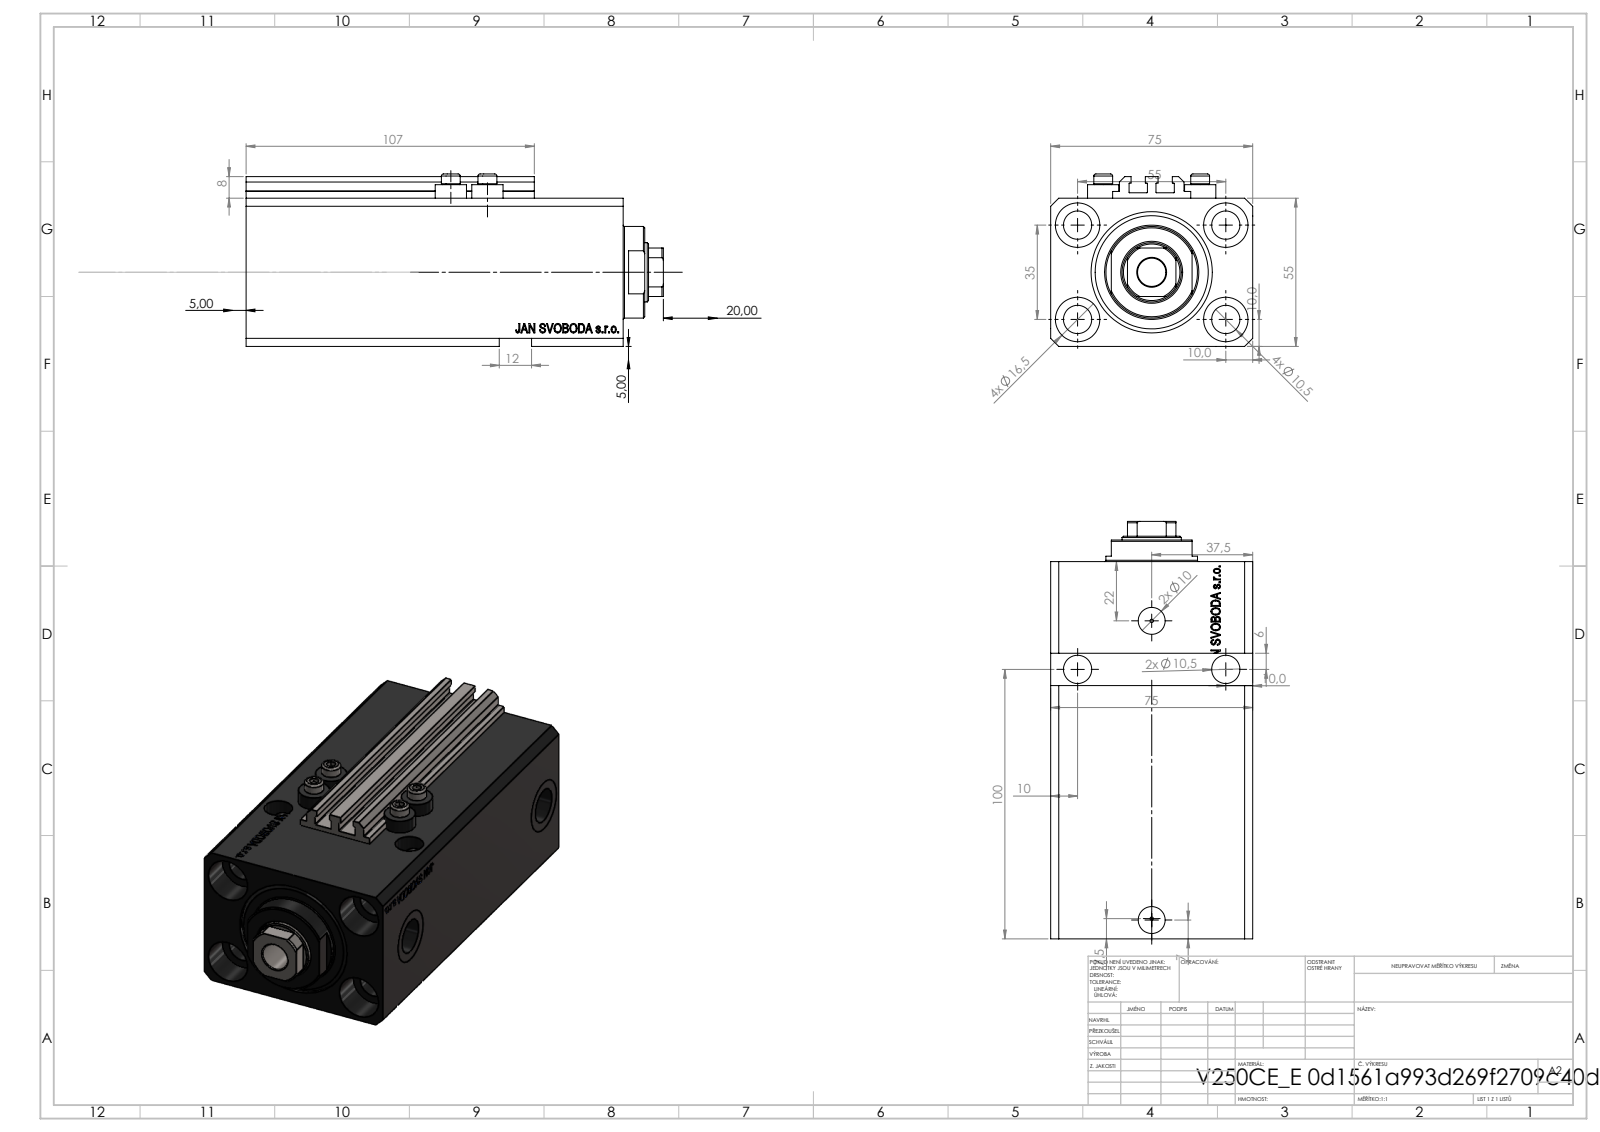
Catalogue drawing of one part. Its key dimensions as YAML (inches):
part_name: "V250CE_VC_E; ALLEN BOLT V250CE; V250CE_C_VCP; V250CE_E"
step_written_by: "SolidWorks 2019 (CONFIG_CONTROL_DESIGN)"
units: inches
bodies: {solids: 8, faces: 1064, planar: 514, cylindrical: 126, other: 424}
overall_size: [6.098, 2.953, 2.52]
volume: 30
surface_area: 180.4
round_holes:
  - {diameter: 0.413, count: 7}
  - {diameter: 0.049, count: 4}
  - {diameter: 0.157, count: 4}
  - {diameter: 0.65, count: 4}
  - {diameter: 0.394, count: 2}
  - {diameter: 0.518, count: 2}
  - {diameter: 0.787, count: 2}
  - {diameter: 0.866, count: 1}
  - {diameter: 1.26, count: 1}
  - {diameter: 1.772, count: 1}
round_bosses_or_shafts:
  - {diameter: 0.457, count: 4}
  - {diameter: 0.276, count: 4}
  - {diameter: 1.339, count: 1}
partial_cylinders:
  - {radius: 0.008, count: 10}
  - {radius: 0.413, count: 1}
face_to_face_distances: [2.165, 2.953, 5.512, 4.445, 1.067, 0.118, 0.39, 2.244, 4.055, 5.122]
hole_center_spacings: [1.283, 2.165, 0.535, 0.555, 1.016, 1.294, 1.324, 1.378]
